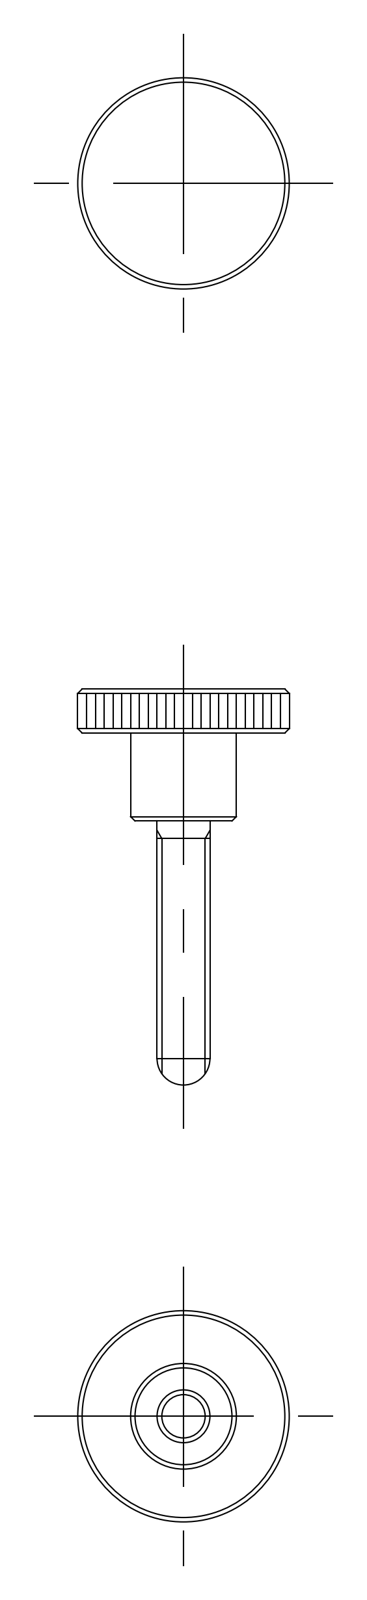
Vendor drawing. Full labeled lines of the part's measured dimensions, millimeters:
Part name (STEP PRODUCT): knob
STEP written by: CADfix (AUTOMOTIVE_DESIGN)
Units: millimetres
Bodies: 1 solid, 16 faces (0 planar, 0 cylindrical, 16 other)
Overall size (bounding box): 45 × 24 × 24
Volume: 4 197 mm³ · Surface area: 2 140 mm²
